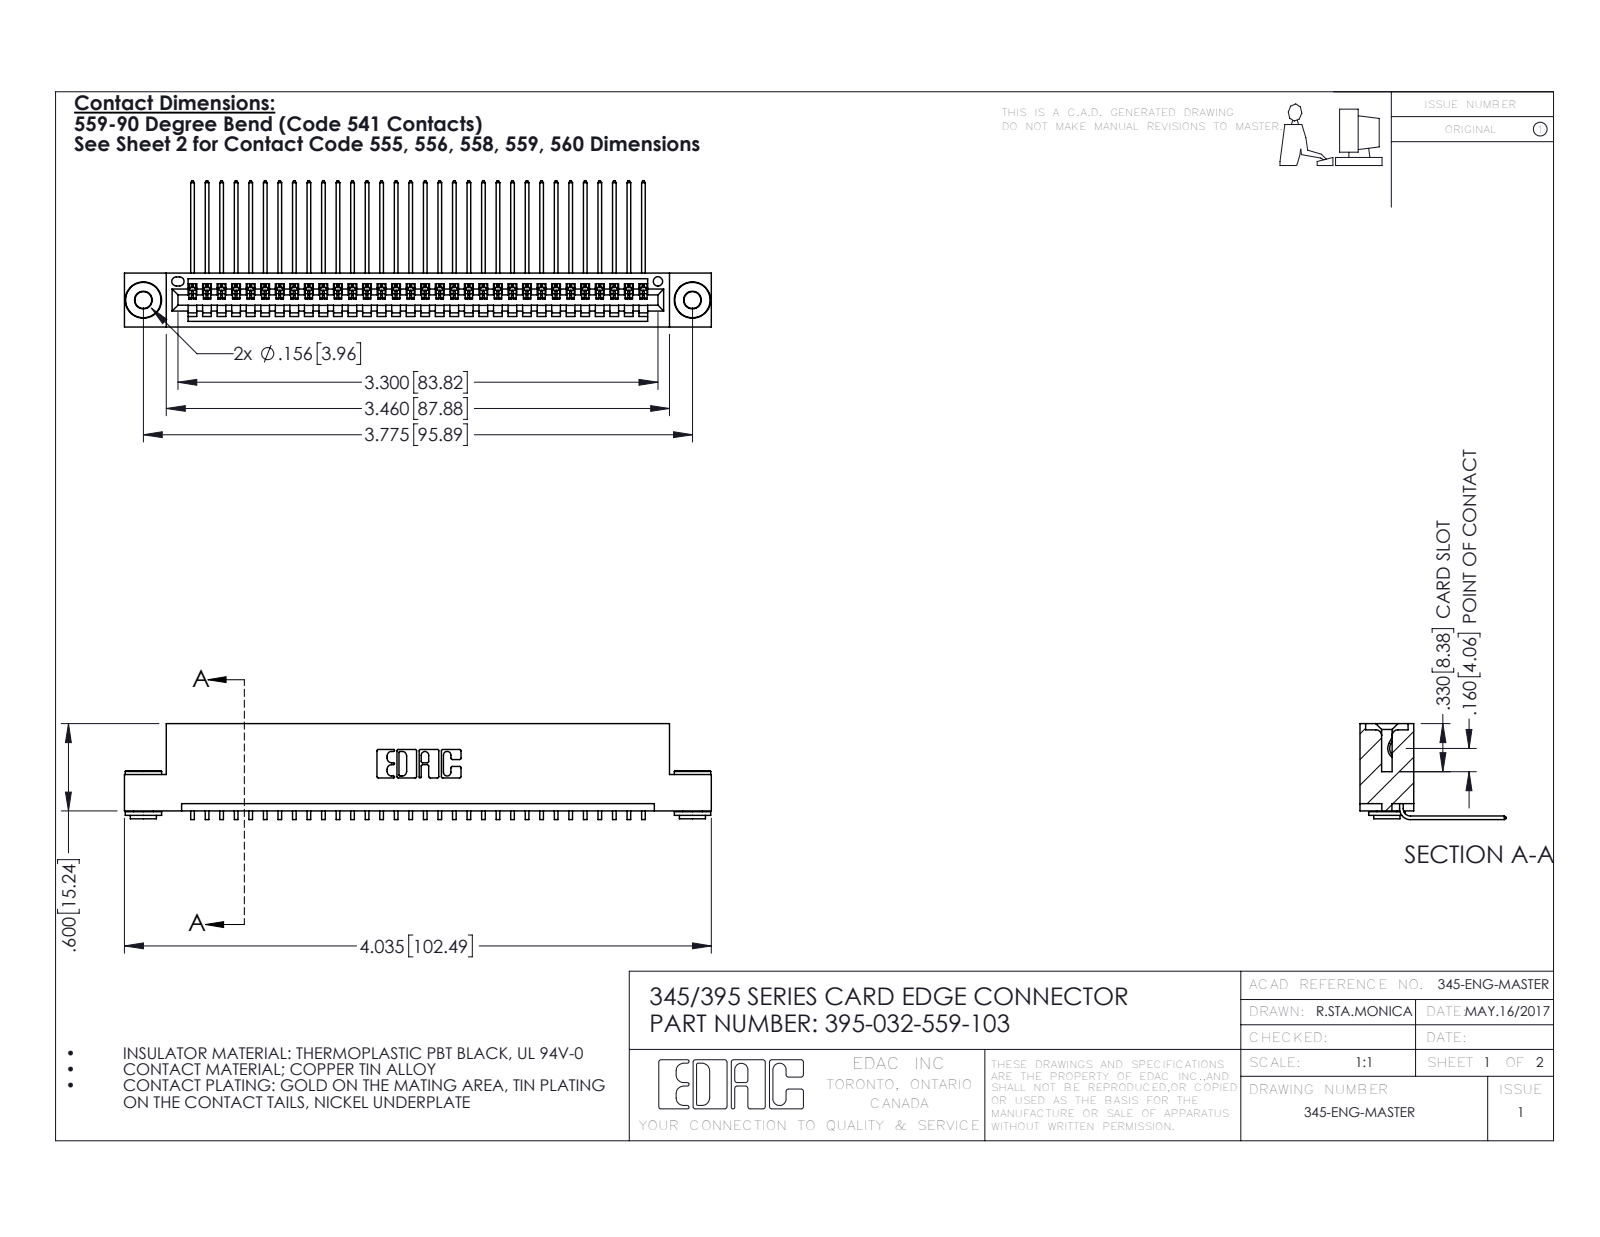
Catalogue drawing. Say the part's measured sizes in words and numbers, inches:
The part is named "345 Part_Flush Mounting Lugs - 0.156 Dia-TH; 345-250-002_345-250-002-102; 395-032-559-103; 345-292-001_558 559 Tail - 1". Its 3-D file was written by "SolidWorks 2016 (CONFIG_CONTROL_DESIGN)". It is 35 solids with 2084 faces: 1434 planar, 642 cylindrical and 8 other. Overall it measures 4.035 by 1.005 by 0.659 inches. Its volume is 0.597 cubic inches and its surface area 21.23 square inches. Round holes: 2 of diameter 0.116, 2 of diameter 0.156, 1 of diameter 0.064. Round bosses or shafts: 2 of diameter 0.25, 2 of diameter 0.18, 2 of diameter 0.136. Partial cylindrical surfaces (rounded edges, fillets, slot ends): 64 of radius 0.006, 22 of radius 0.01, 6 of radius 0.007, 6 of radius 0.031, 3 of radius 0.026, 2 of radius 0.031, 2 of radius 0.04, 1 of radius 0.014. The main face-to-face distances are 0.072, 0.298, 0.37, 0.2, 0.025, 0.098, 0.272, 0.225, 0.149, 0.072. The hole center spacings are 0.27, 3.54, 3.775.
